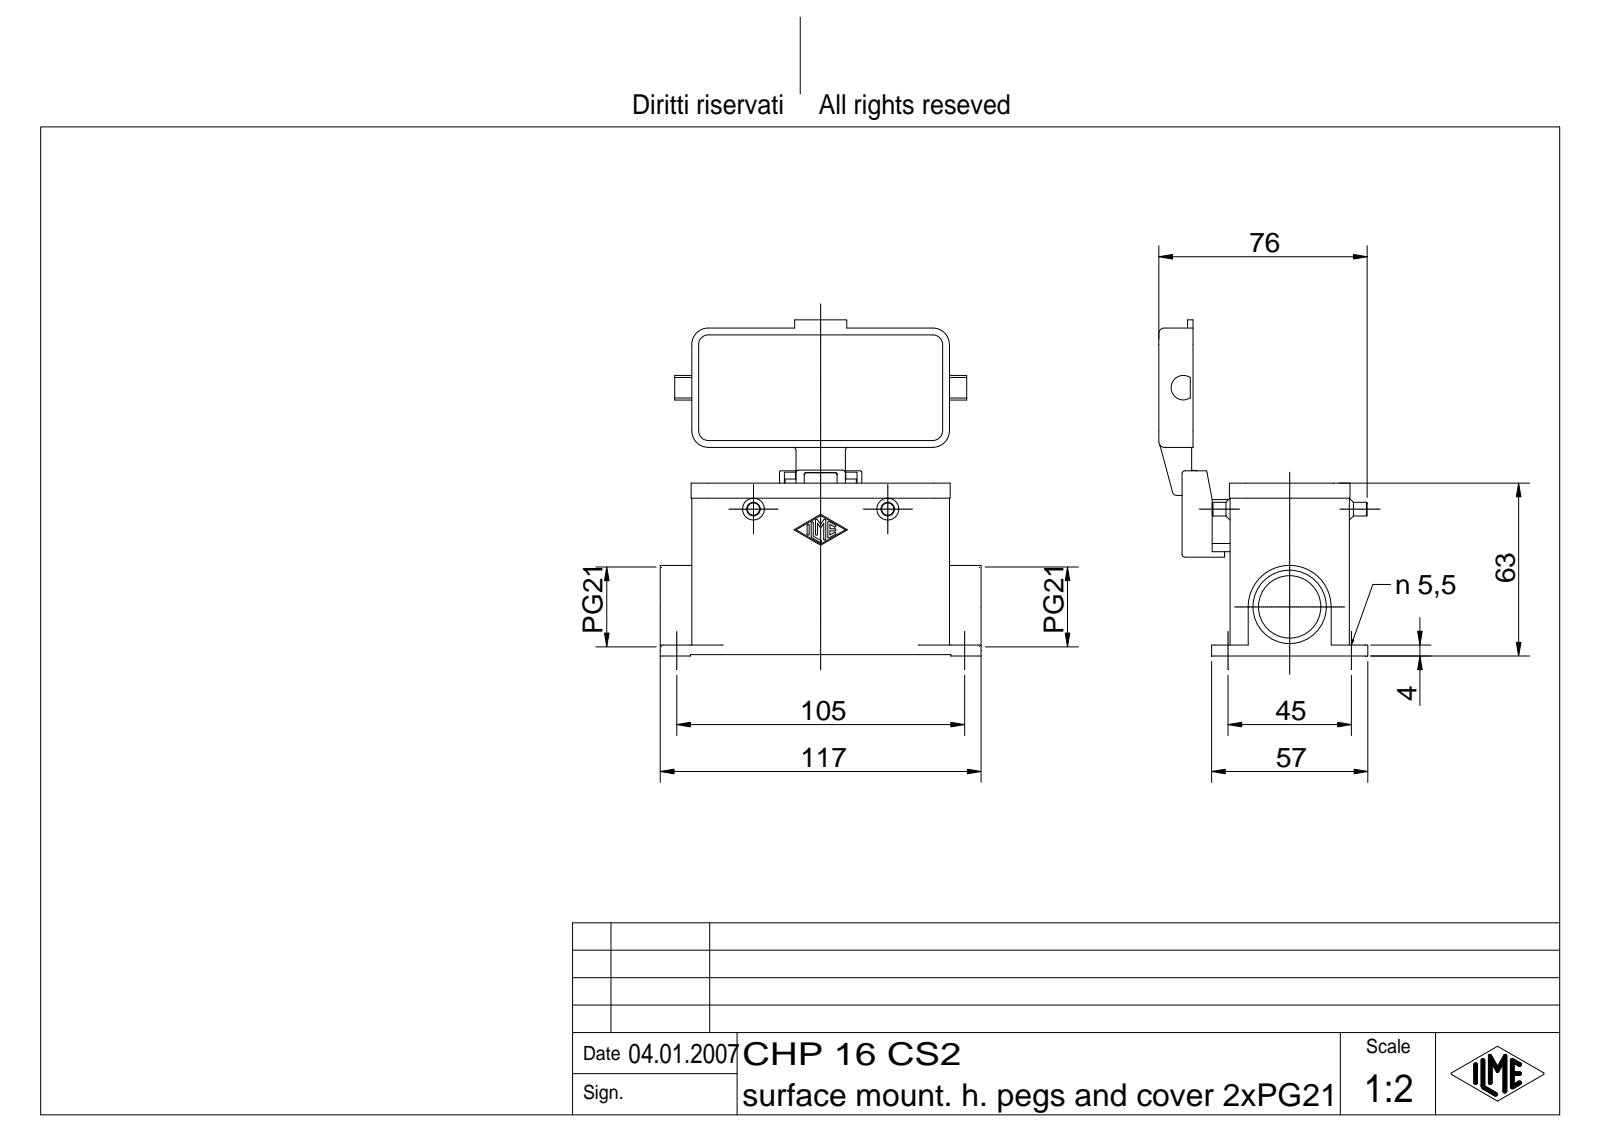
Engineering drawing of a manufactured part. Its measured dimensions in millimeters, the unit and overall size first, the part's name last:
Units: millimetres
Overall size (bounding box): 122.5 × 117 × 76.25
Round holes (diameter × count): ⌀5.5 ×4, ⌀4 ×1, ⌀5 ×1, ⌀22.78 ×1, ⌀26.78 ×1
Round bosses / shafts (diameter × count): ⌀5 ×2, ⌀3 ×2, ⌀7 ×1, ⌀4 ×1
Partial cylindrical surfaces — rounded edges, fillets, slot ends (radius × count): R1 ×26, R0.38 ×14, R6 ×12, R0.5 ×9, R0.7 ×8, R2 ×8, R3 ×4, R3.5 ×4
Main face-to-face distances: 3, 40.5, 3.5, 43.5, 29, 63, 37.5, 22.5, 69.5, 66.5
Hole centre spacings: 45, 105, 114.24
Volume: 115 475 mm³ · Surface area: 65 768 mm²
Bodies: 2 solids, 474 faces (177 planar, 177 cylindrical, 120 other)
Part name (STEP PRODUCT): CHP 16 CS2
STEP written by: Autodesk Inventor 7 (AUTOMOTIVE_DESIGN)
